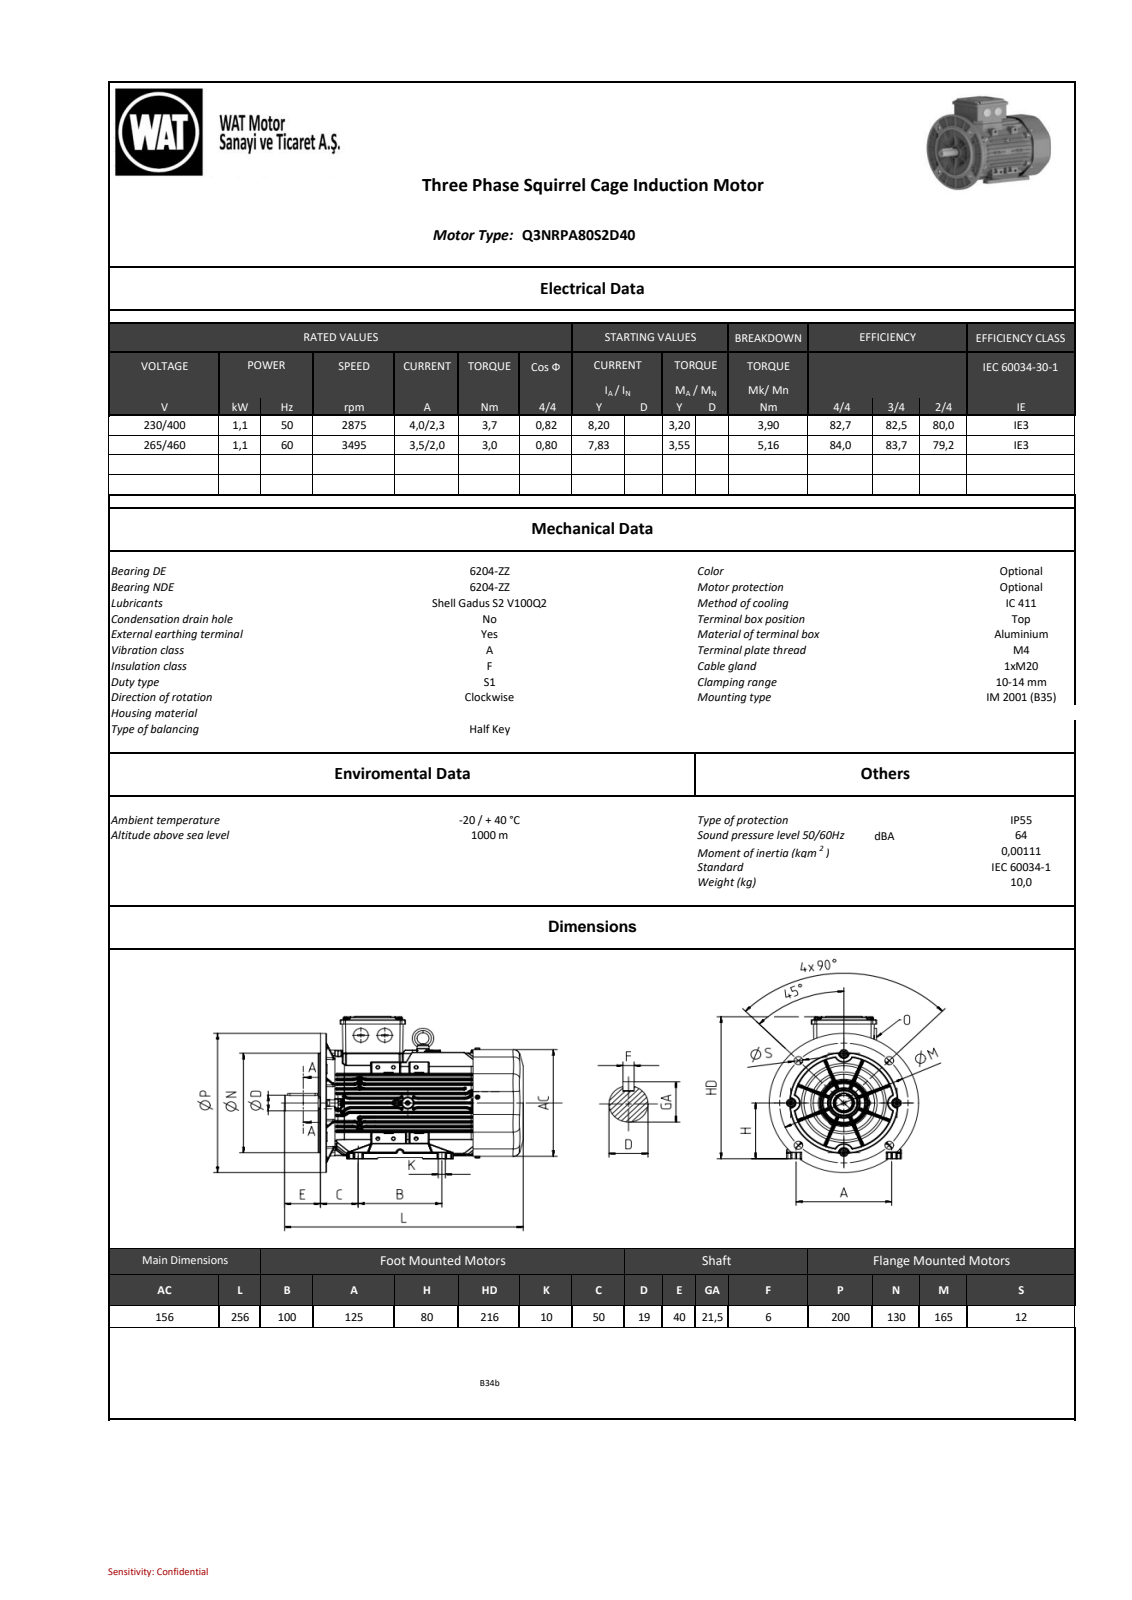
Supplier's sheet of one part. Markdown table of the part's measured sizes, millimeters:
| quantity | value |
| --- | --- |
| part name | 260320808B12lih2 |
| STEP written by | SIEMENS PLM Software NX 11.0 (AUTOMOTIVE_DESIGN) |
| units | millimeters |
| bodies | 1 solid, 5792 faces (1435 planar, 2276 cylindrical, 2081 other) |
| overall size | 255.71 × 205.95 × 198 |
| round holes (diameter × count) | 4 × 1, 4.2 × 1, 4.5 × 1, 6.4 × 1, 13 × 1, 27.8 × 1, 28 × 1 |
| round bosses / shafts (diameter × count) | 8 × 7, 5 × 7, 8.5 × 4, 20 × 2, 134.4 × 1, 130 × 1, 29.5 × 1, 19 × 1 |
| partial cylindrical surfaces (radius × count) | 0.5 × 592, 1 × 462, 0.8 × 159, 0.4 × 103, 0.2 × 53, 0.25 × 45, 1.5 × 26, 2 × 26 |
| main face-to-face distances | 6, 0.8, 209.71, 215.71, 30, 36.21, 173.5, 179.5, 3, 206.71 |
| hole center spacings | 106.22 |
